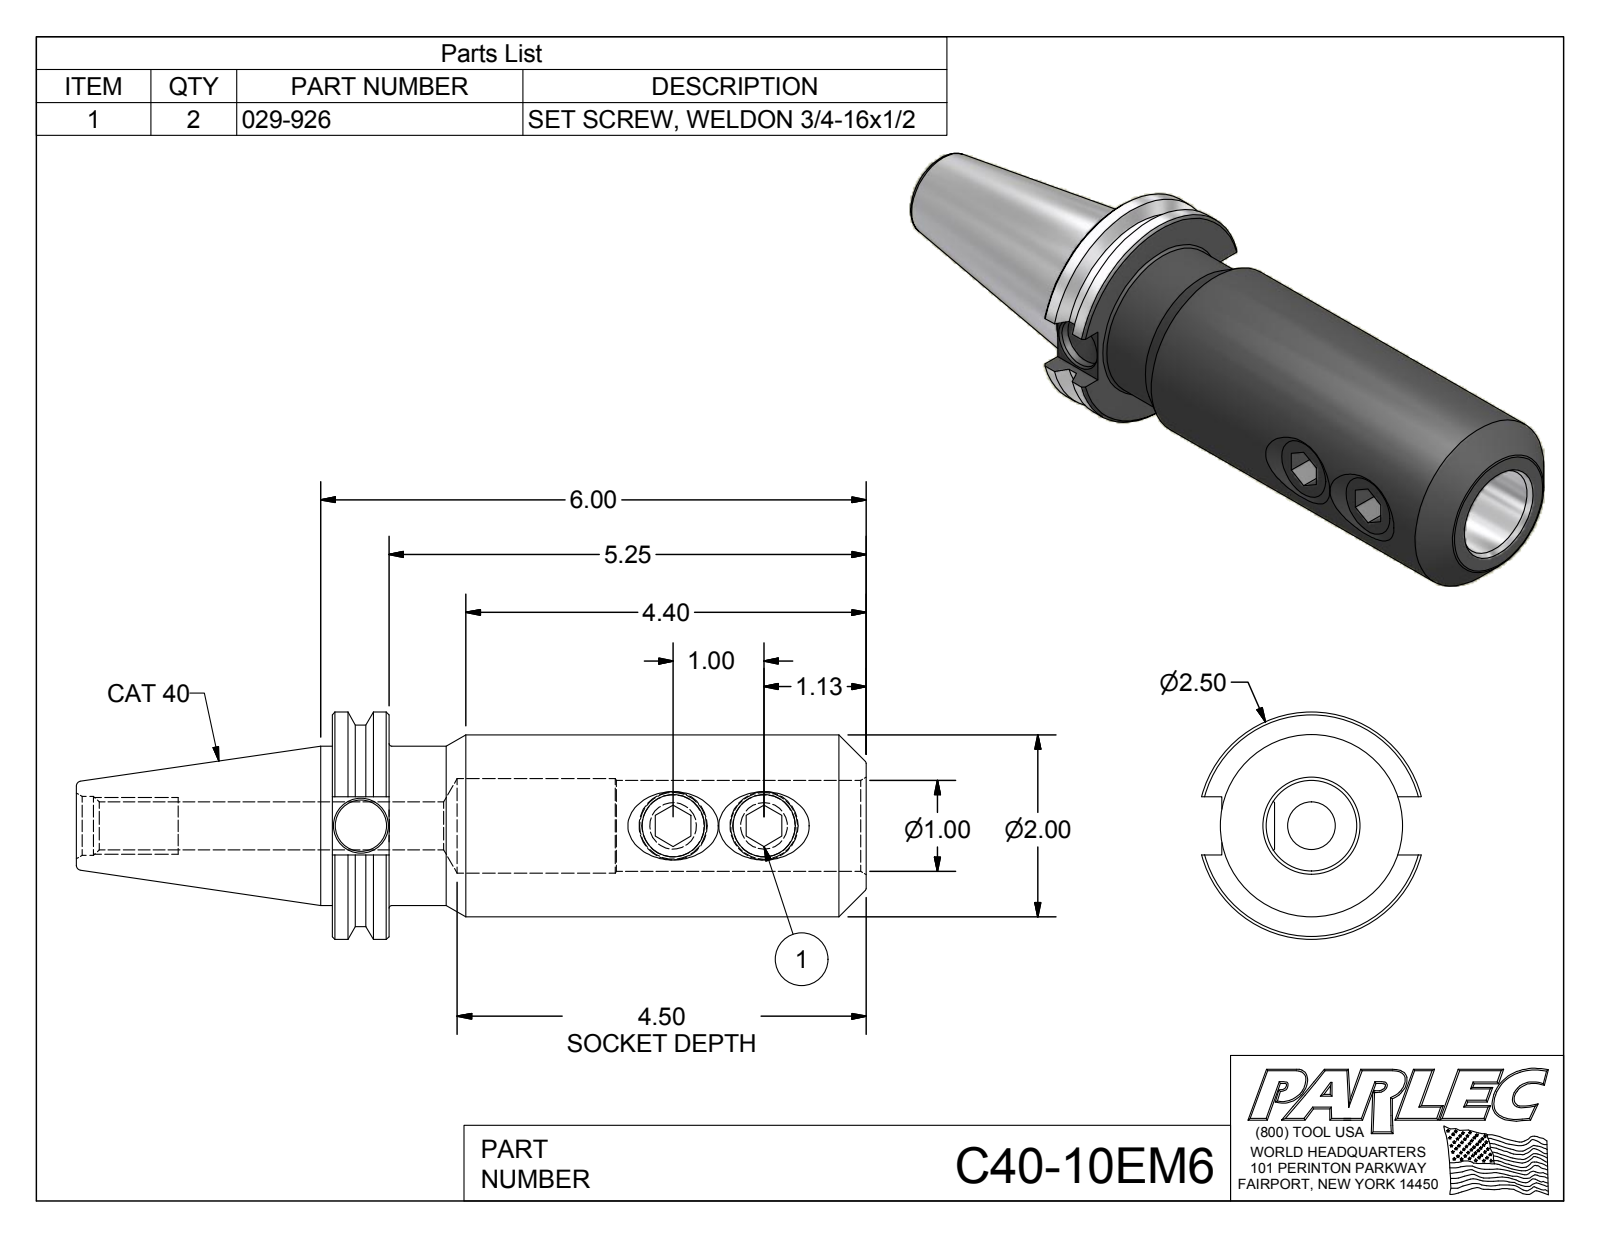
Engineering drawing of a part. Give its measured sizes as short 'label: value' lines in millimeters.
name: C40-10EM6; C40-10EM6-1; 029-926
written by: Autodesk Inventor 2012 (AUTOMOTIVE_DESIGN)
unit: mm
bodies: 3 solids, 73 faces (28 planar, 18 cylindrical, 27 other)
size: 220.7 × 63.5 × 61.4
volume: 292 800 mm³; area: 54 310 mm²
holes: 2× ⌀17.3, 1× ⌀13.4, 1× ⌀14.3, 1× ⌀16.5, 1× ⌀25.4, 1× ⌀26.4
bosses: 2× ⌀19.1, 1× ⌀63.5, 1× ⌀56.4, 1× ⌀50.8, 1× ⌀44.5
face distances: 15.9, 12.7, 10, 149.2, 133.4, 32.9, 45.6, 33.6, 16.3, 0.7
hole spacings: 25.4, 87.2, 112.6
